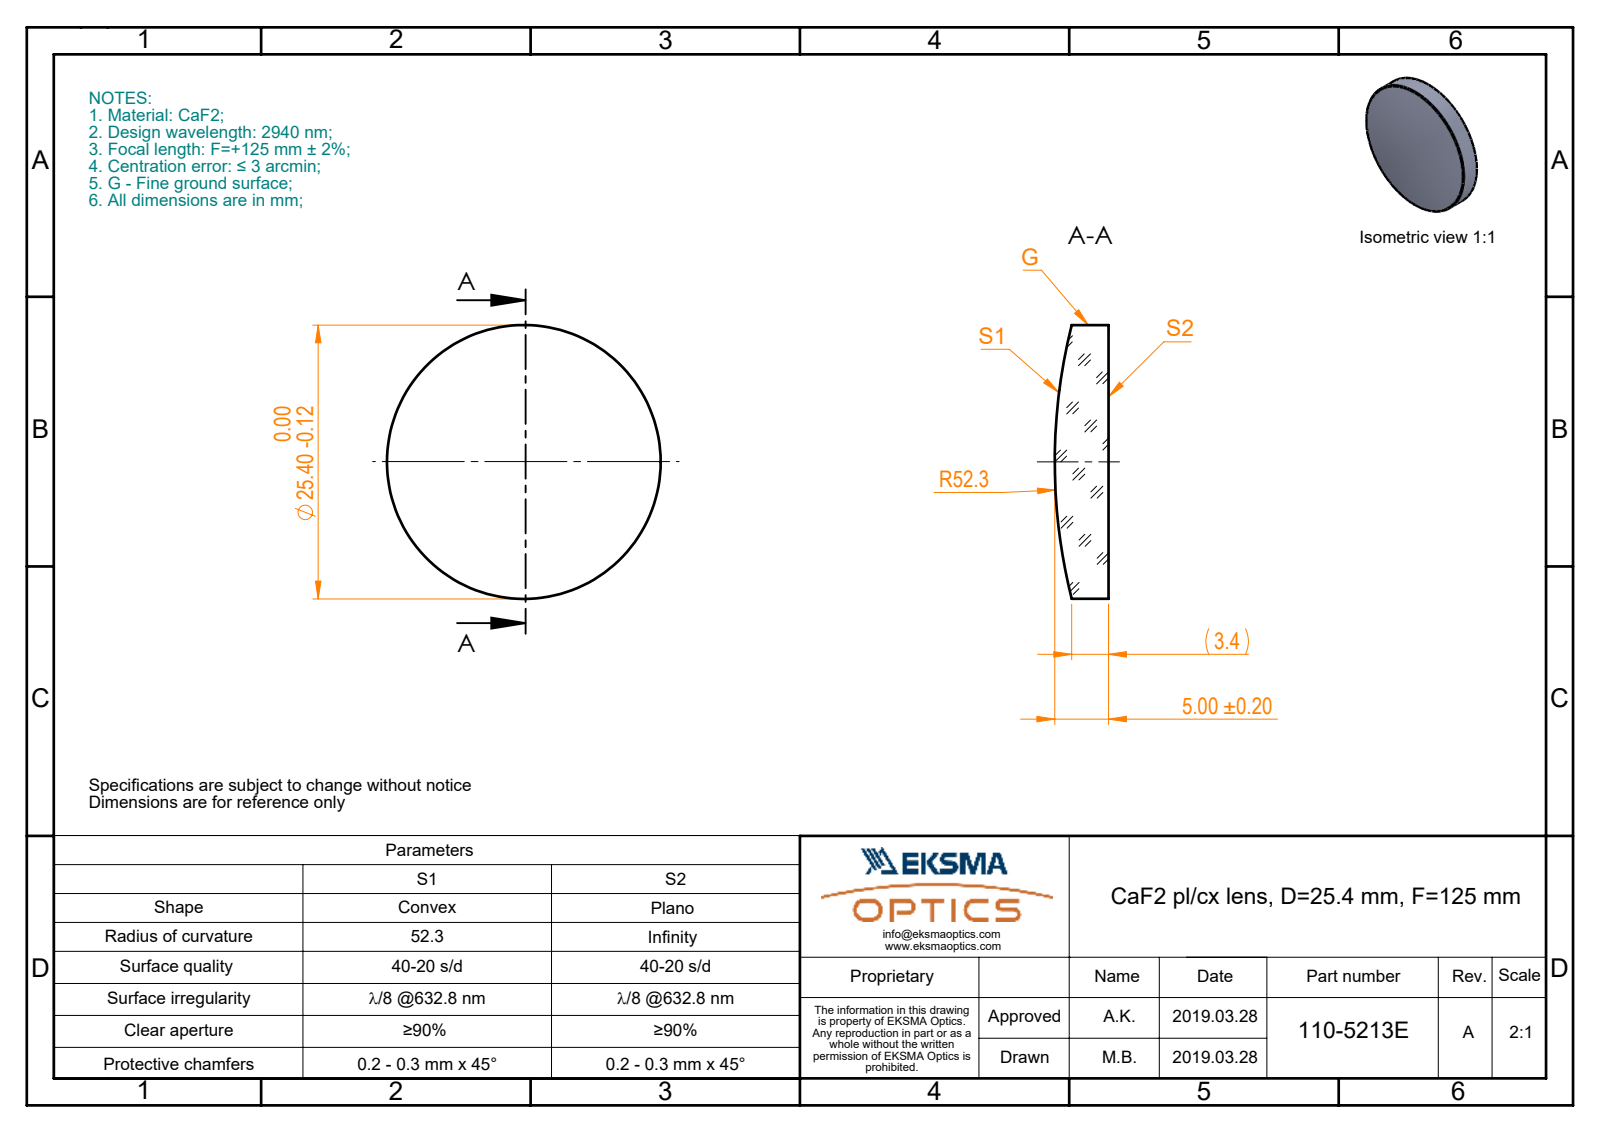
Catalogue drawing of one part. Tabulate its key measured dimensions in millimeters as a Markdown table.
| quantity | value |
| --- | --- |
| part name | 110-5213E CaF2 pl-cx 25.4 F125 |
| STEP written by | SolidWorks 2017 (CONFIG_CONTROL_DESIGN) |
| units | millimeters |
| bodies | 1 solid, 5 faces (1 planar, 2 cylindrical, 2 other) |
| overall size | 25.4 × 25.4 × 5 |
| volume | 2 139 mm³ |
| surface area | 1 295 mm² |
| round bosses / shafts (diameter × count) | 25.4 × 1 |
